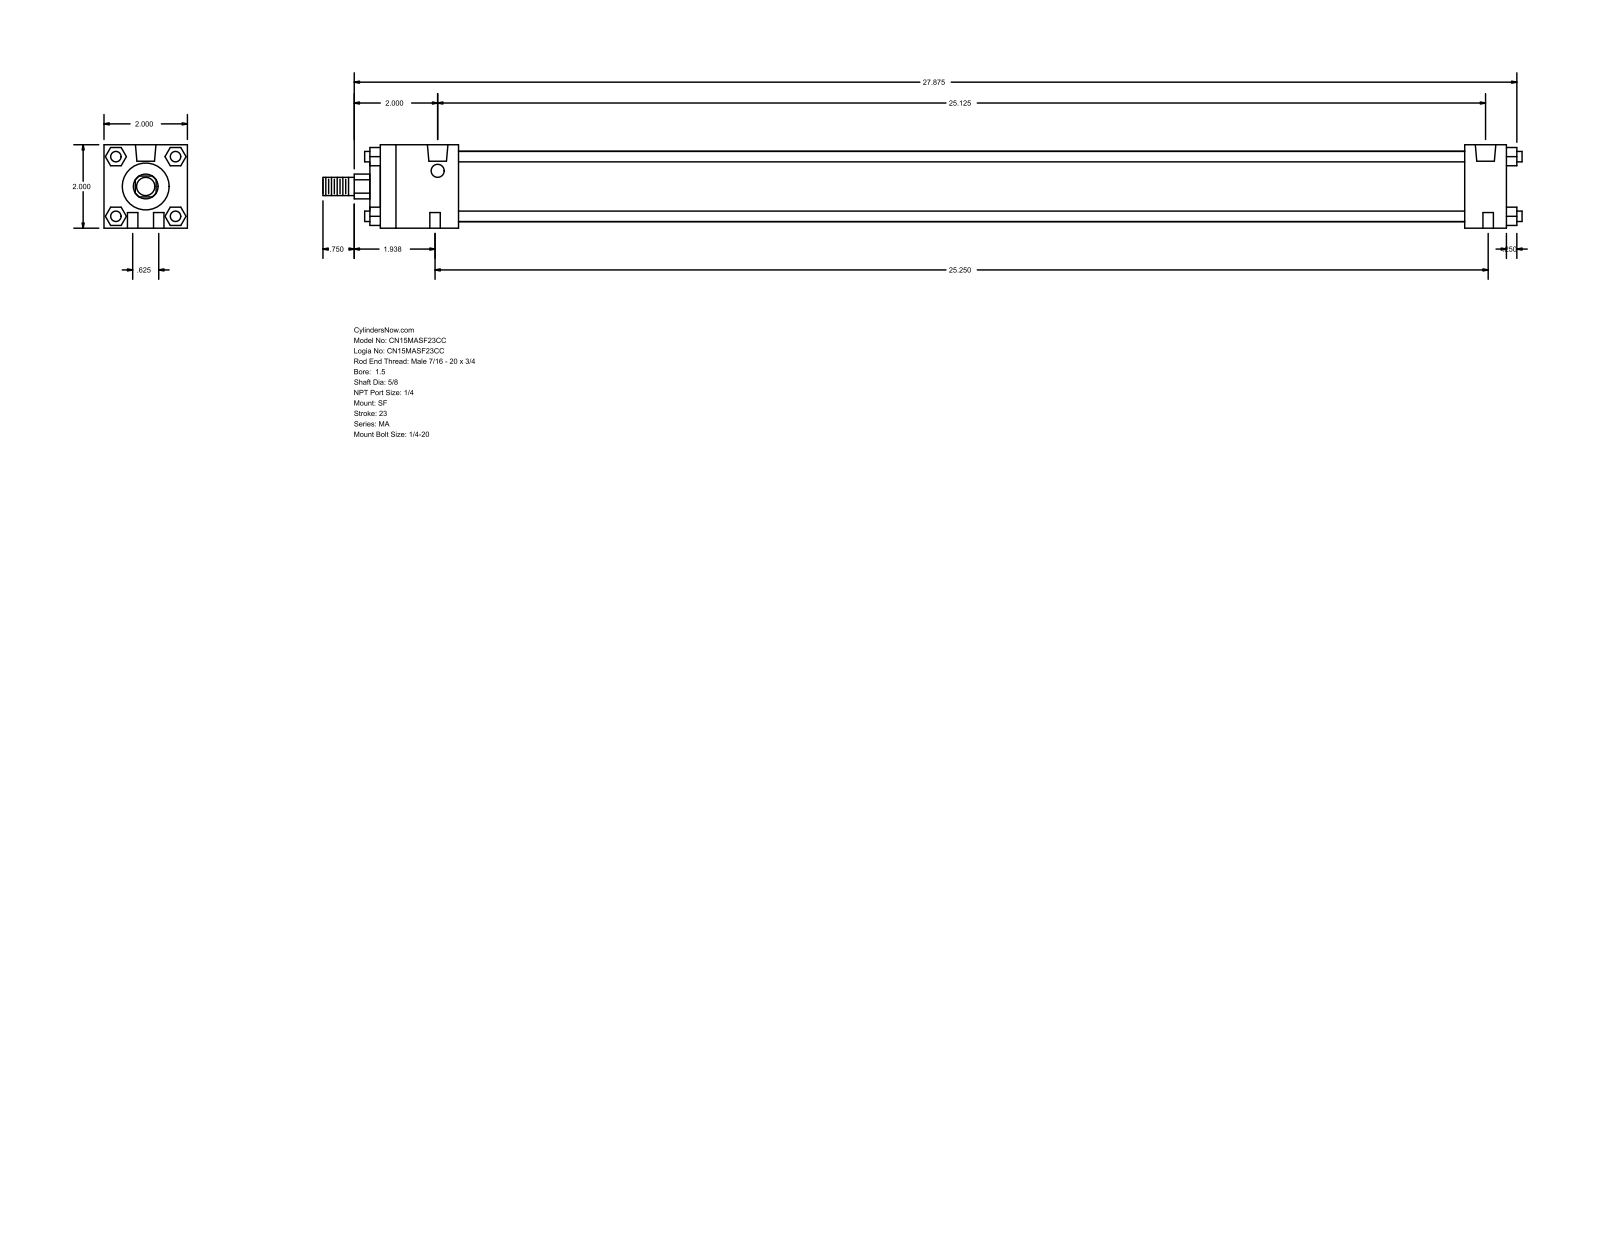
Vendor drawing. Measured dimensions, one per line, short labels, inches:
name: MA_SF__0150_0.625
written by: GSSL Pune (CONFIG_CONTROL_DESIGN)
unit: in
bodies: 0 solids, 124 faces (94 planar, 30 cylindrical, 0 other)
size: 28.75 × 2 × 2
holes: 4× ⌀0.25, 2× ⌀0.313, 2× ⌀0.492
bosses: 4× ⌀0.25, 1× ⌀1.69, 1× ⌀1.125, 1× ⌀0.625, 1× ⌀0.437
rounds: 1× R0.297
face distances: 2, 27, 0.25, 1, 27.25, 1.875, 26, 24.125, 25.125, 2.125
hole spacings: 0.319, 0.625, 25.125, 25.189, 25.19, 25.25, 25.258
